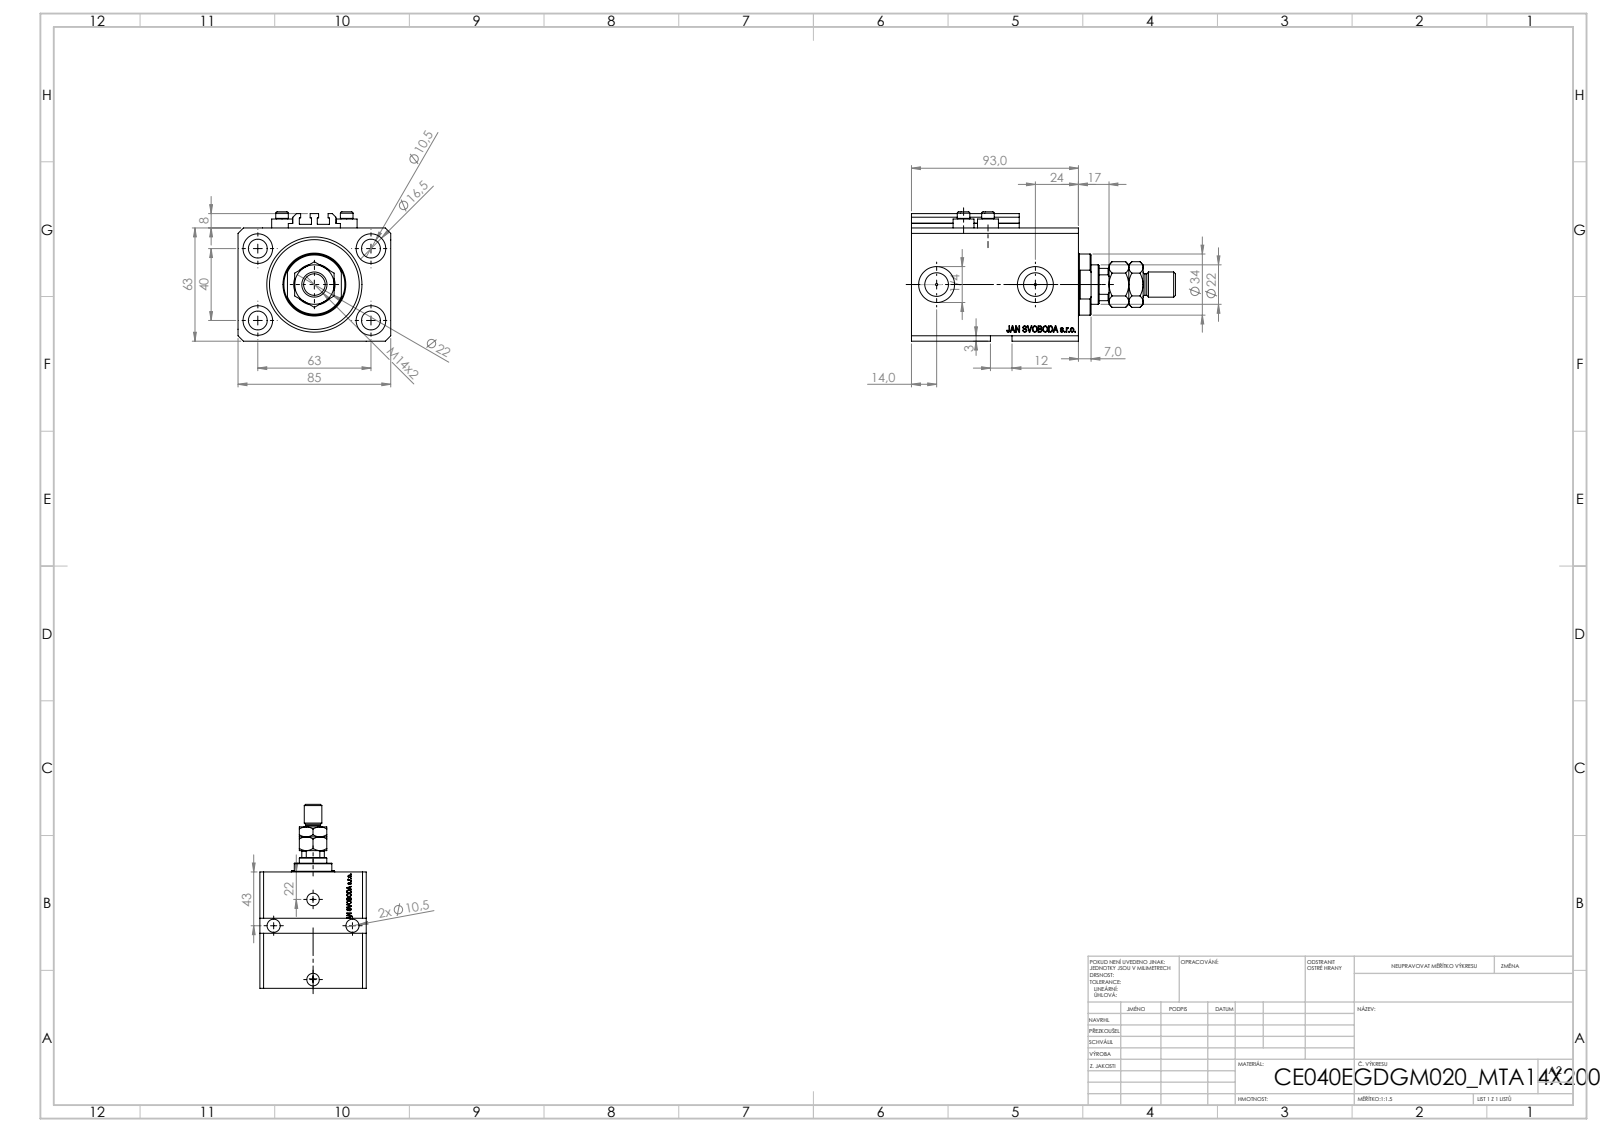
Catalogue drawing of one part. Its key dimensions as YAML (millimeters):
part_name: "V250CE_E_Body; V250CE_C_VCP; ALLEN BOLT V250CE; V250CE_VC_E (+1 more)"
step_written_by: "SolidWorks 2019 (CONFIG_CONTROL_DESIGN)"
units: millimeters
bodies: {solids: 9, faces: 1152, planar: 554, cylindrical: 142, other: 456}
overall_size: [146.9, 85, 72]
volume: 444156
surface_area: 102123
round_holes:
  - {diameter: 10.5, count: 6}
  - {diameter: 1.25, count: 4}
  - {diameter: 4, count: 4}
  - {diameter: 16.5, count: 4}
  - {diameter: 10, count: 2}
  - {diameter: 13.16, count: 2}
  - {diameter: 20, count: 2}
  - {diameter: 12.5, count: 1}
  - {diameter: 22, count: 1}
  - {diameter: 40, count: 1}
  - {diameter: 53, count: 1}
round_bosses_or_shafts:
  - {diameter: 11.6, count: 4}
  - {diameter: 7, count: 4}
  - {diameter: 34, count: 1}
  - {diameter: 14, count: 1}
  - {diameter: 12, count: 1}
partial_cylinders:
  - {radius: 0.2, count: 10}
  - {radius: 10.5, count: 1}
face_to_face_distances: [63, 85, 93, 65.9, 54.5, 27.1, 11.4, 81.6, 3, 44]
hole_center_spacings: [37.31, 63, 13.6, 15.4, 24.96, 28.02, 28.43, 33.62]
